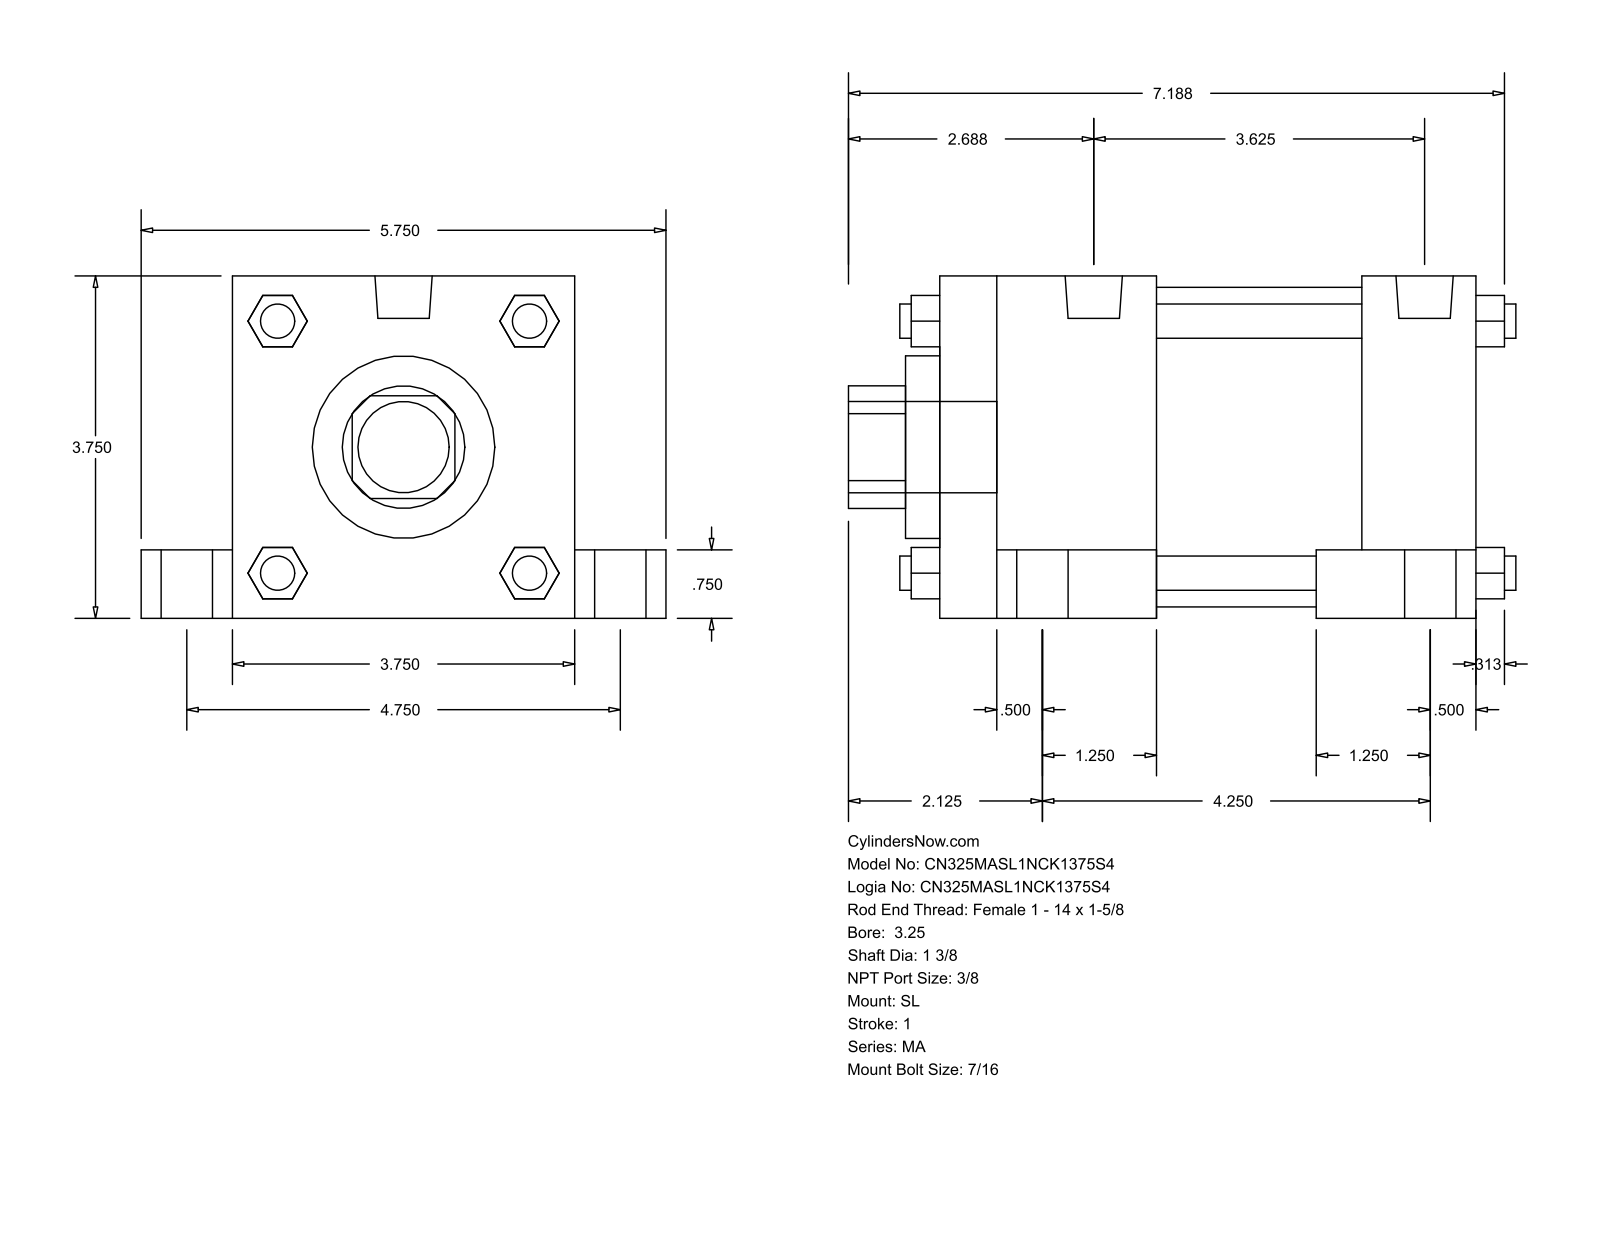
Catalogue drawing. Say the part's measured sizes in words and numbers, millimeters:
The part is named "MA_SL__0325_1.375". Its 3-D file was written by "GSSL Pune (CONFIG_CONTROL_DESIGN)". It is 0 solids with 148 faces: 112 planar, 36 cylindrical and 0 other. Overall it measures 185.74 by 146.05 by 95.25 millimeters. Round holes: 1 of diameter 34.92, 1 of diameter 50.8, 1 of diameter 88.9. Round bosses or shafts: 4 of diameter 20.64, 4 of diameter 14.29, 4 of diameter 11.11, 4 of diameter 9.53, 2 of diameter 15.93, 1 of diameter 25.4. Partial cylindrical surfaces (rounded edges, fillets, slot ends): 1 of radius 17.06. The main face-to-face distances are 95.24, 149.22, 25.41, 120.65, 117.48, 31.74, 60.32, 57.16, 88.9, 19.05.
